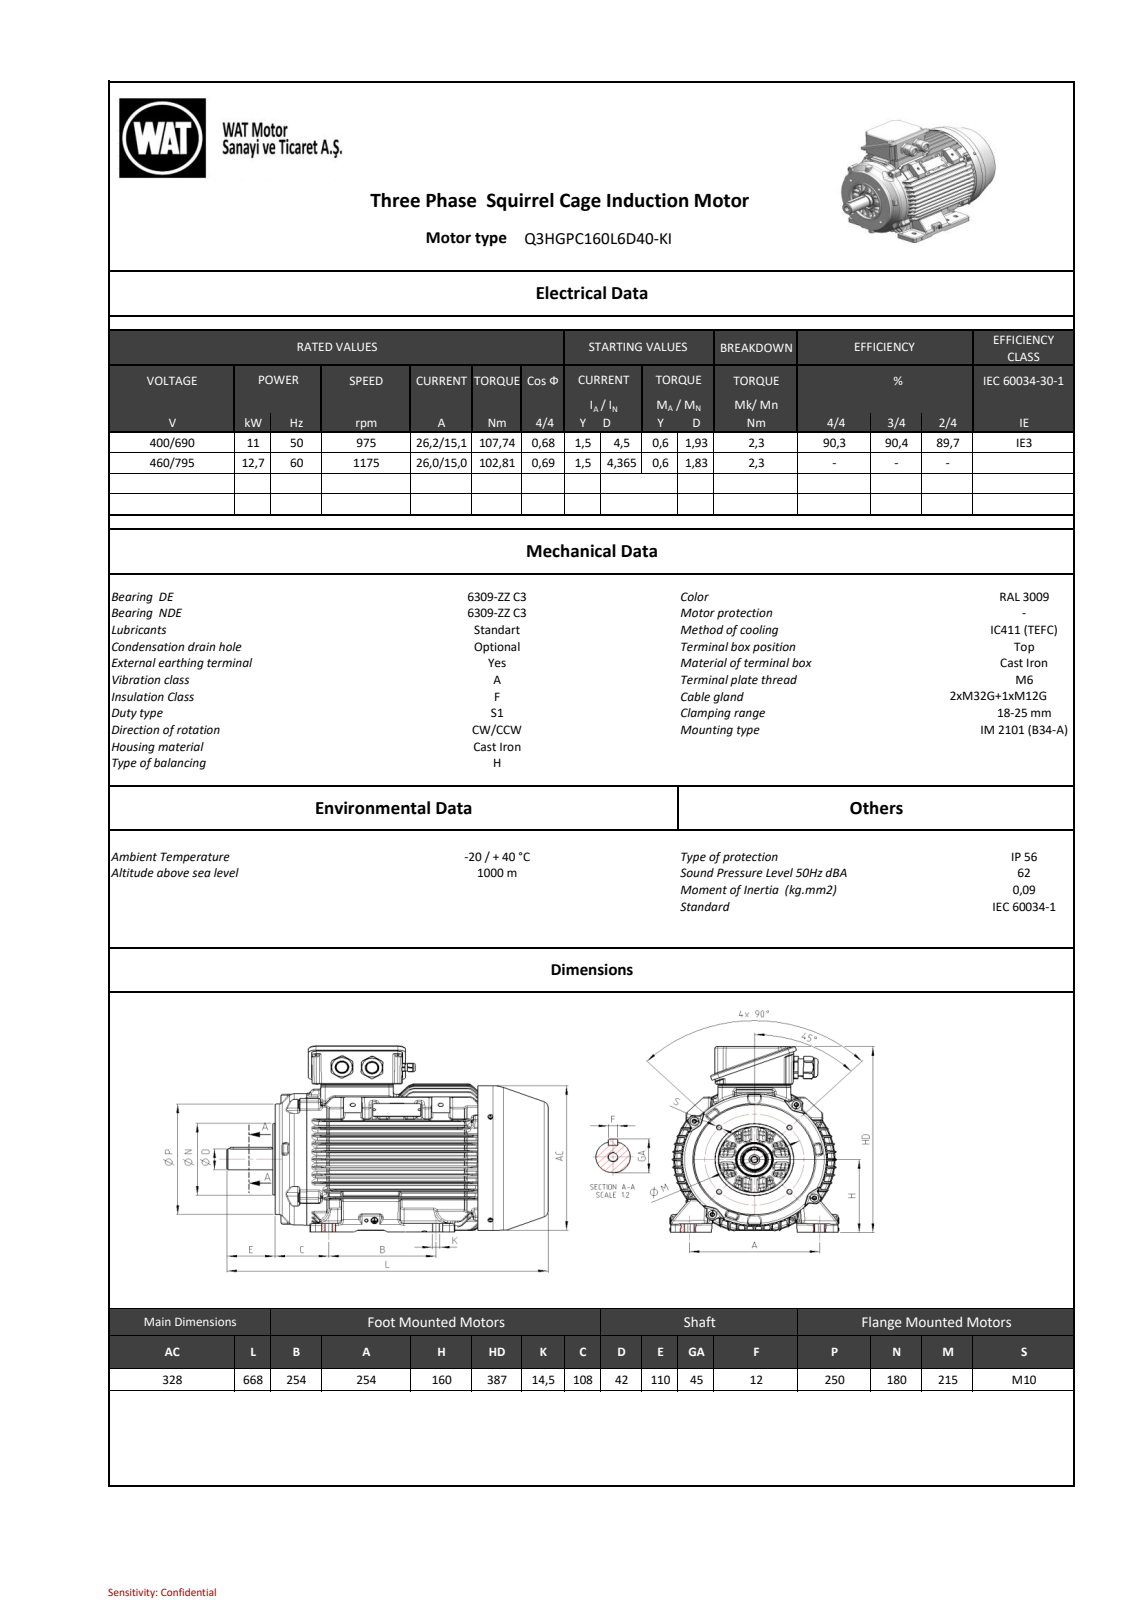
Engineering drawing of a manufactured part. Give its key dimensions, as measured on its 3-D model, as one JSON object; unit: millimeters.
{"part_name": "26000C948E142t3z", "step_written_by": "SIEMENS PLM Software NX 11.0 (AUTOMOTIVE_DESIGN)", "units": "millimeters", "bodies": {"solids": 0, "faces": 6326, "planar": 1217, "cylindrical": 1796, "other": 3313}, "overall_size": [667.5, 388.3, 327.37], "round_holes": [[5.5, 8], [9, 8], [4.2, 7], [5.3, 4], [8.5, 4], [10.9, 2], [5.2, 1], [10, 1], [14, 1], [17, 1], [19, 1], [21, 1]], "round_bosses_or_shafts": [[16, 8], [20, 4], [30, 2], [10, 2], [317, 1], [282, 1], [180, 1], [45, 1]], "partial_cylinders_radius": [[5, 245], [3, 219], [1.5, 112], [4, 112], [1.8, 54], [2, 52], [1, 35], [0.4, 32]], "face_to_face_distances": [137.45, 15.17, 30.42, 122.2, 15.25, 45.73, 106.89, 30.56, 15.31, 107.03], "hole_center_spacings": [136, 42.46, 144, 164.06, 194.08, 203.65, 250.56, 123.22]}
